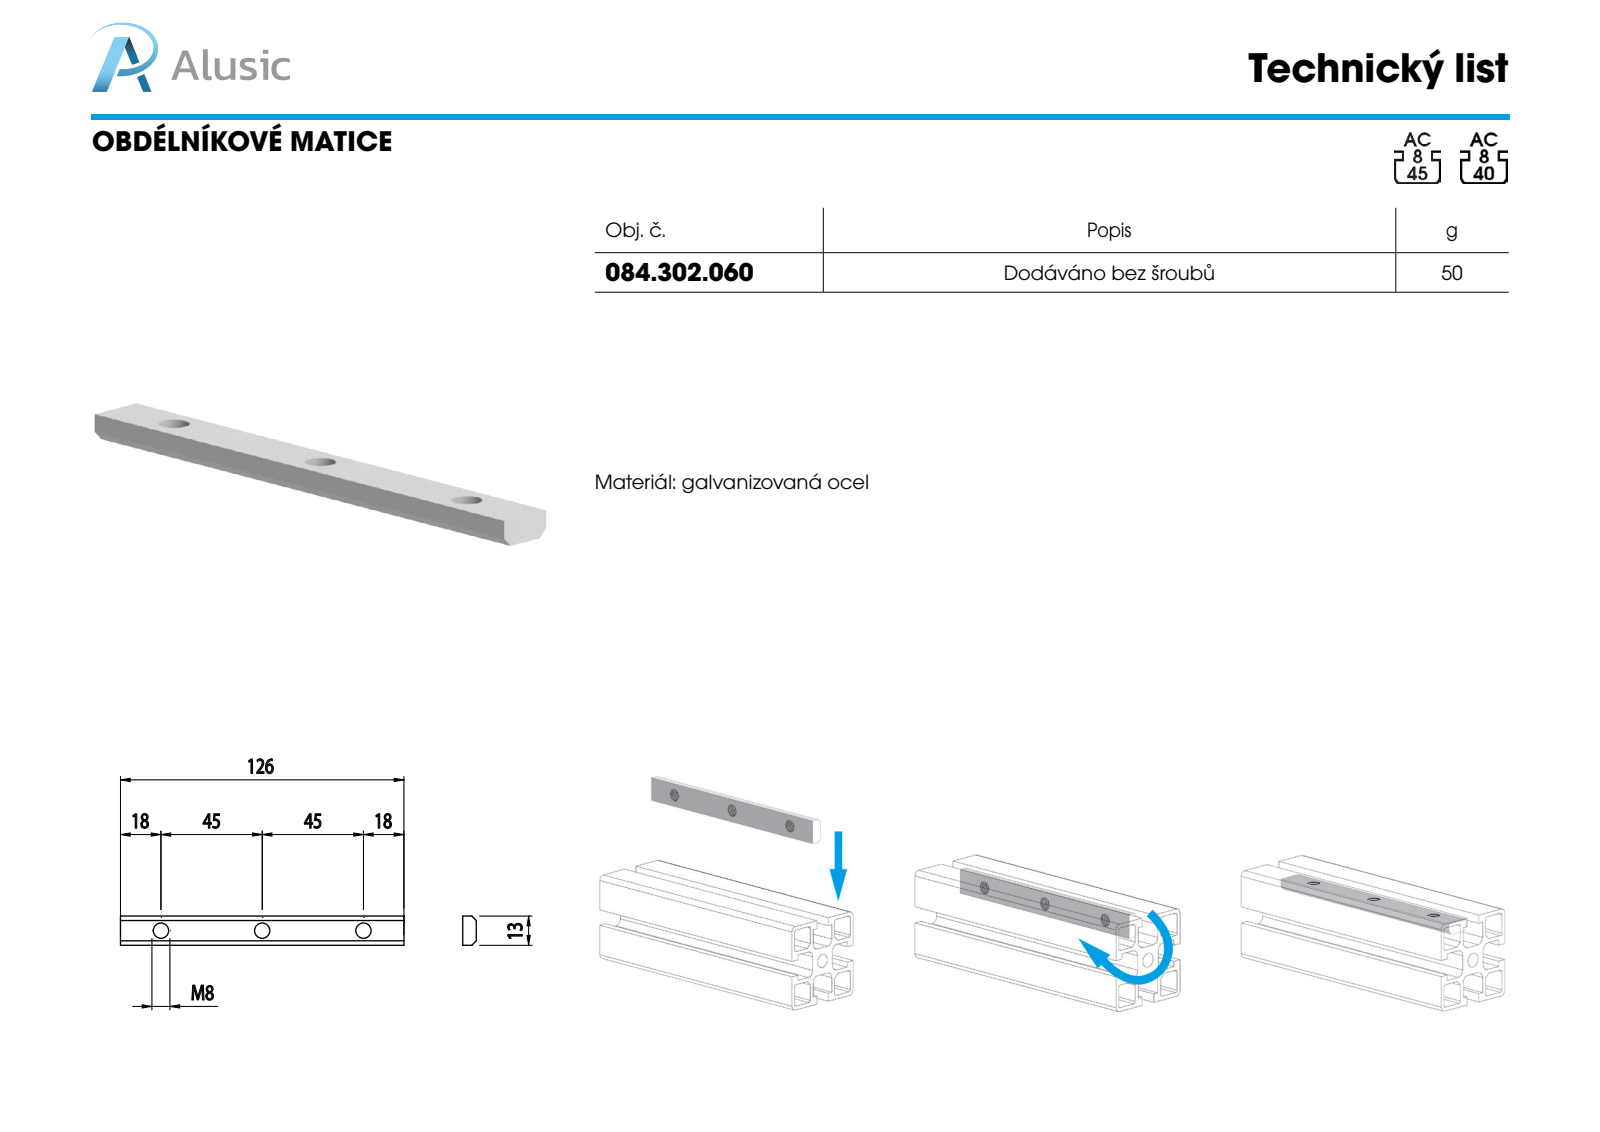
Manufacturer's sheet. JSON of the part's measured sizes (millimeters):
{"part_name": "084.302.060", "step_written_by": "SolidWorks 2012 (CONFIG_CONTROL_DESIGN)", "units": "millimeters", "bodies": {"solids": 1, "faces": 14, "planar": 8, "cylindrical": 6, "other": 0}, "overall_size": [126, 13, 6], "volume_mm3": 8670, "surface_area_mm2": 4807, "round_holes": [[6.8, 3]], "face_to_face_distances": [6, 13, 126], "hole_center_spacings": [45, 90]}
